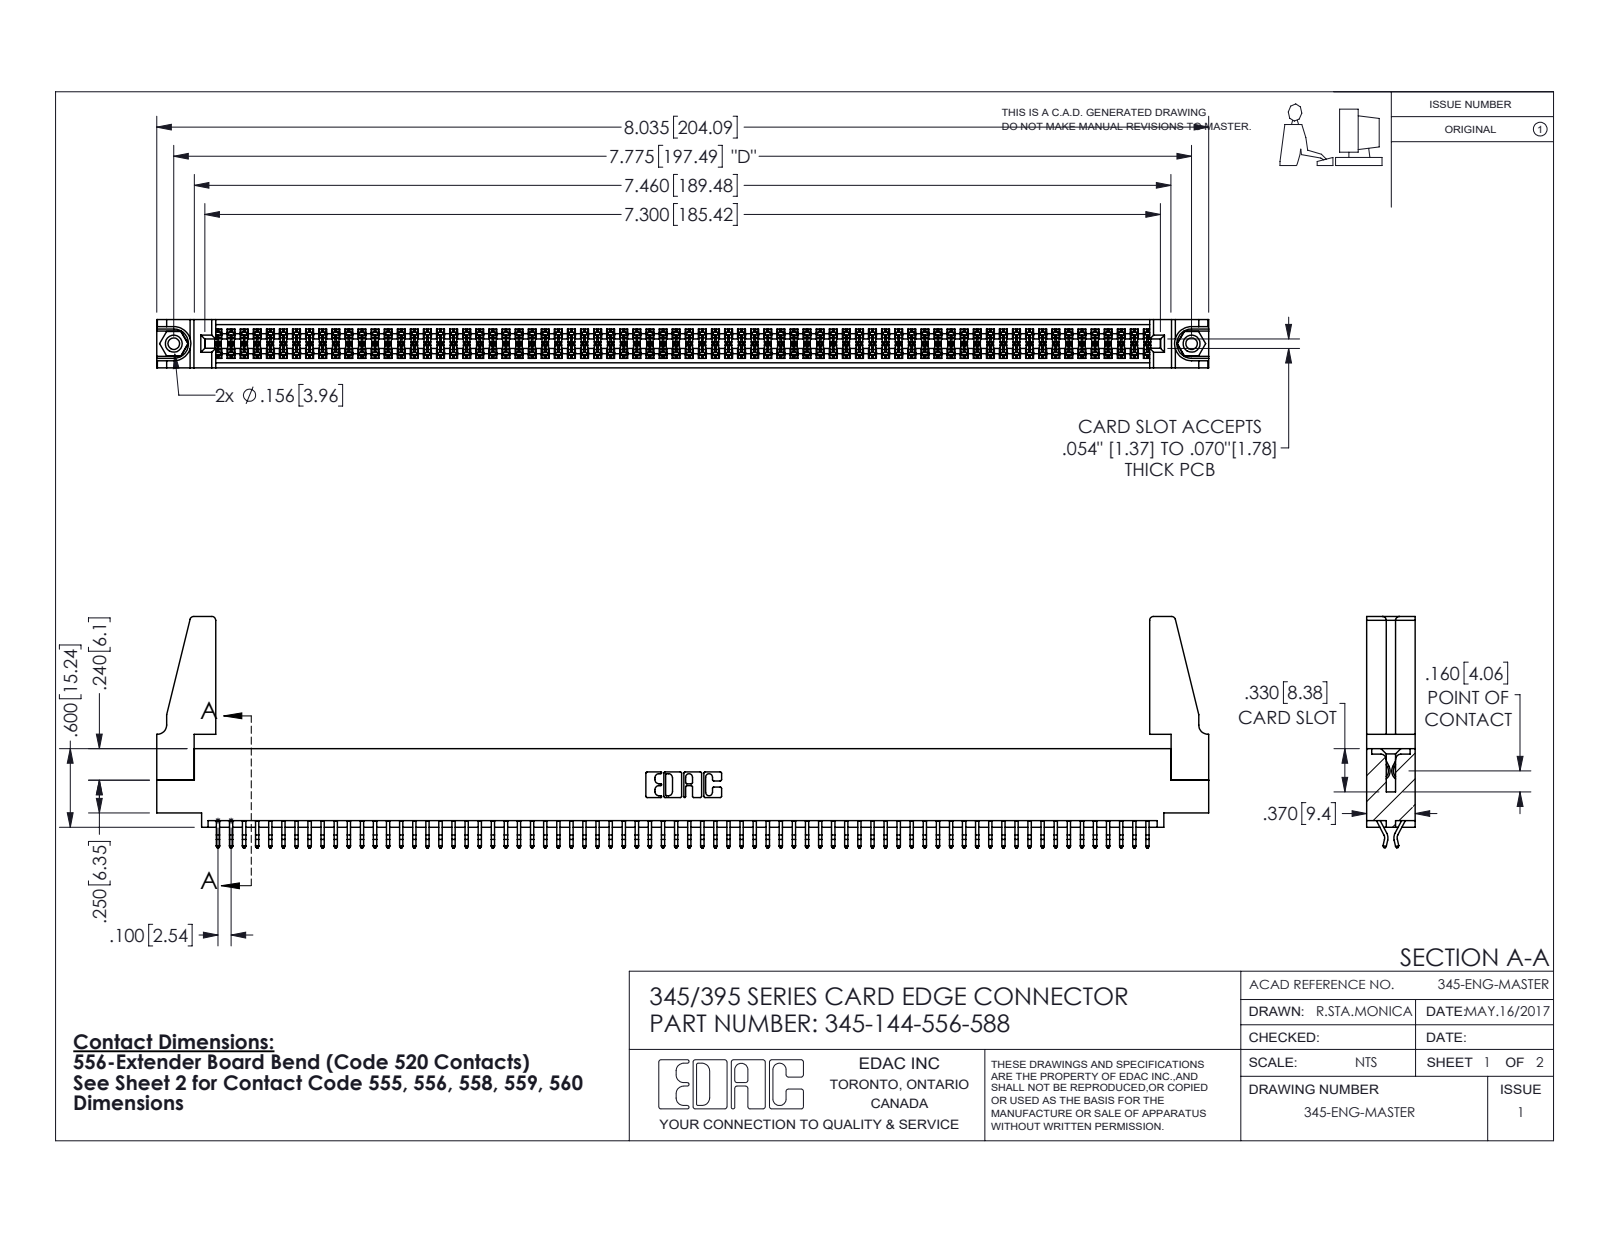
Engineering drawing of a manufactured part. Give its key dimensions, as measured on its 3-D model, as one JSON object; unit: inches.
{"part_name": "345-250-001_345-250-001-102; 345-144-556-588; 345-292-001_556 Tail; 345 Part_0.110 Offset - 0.156 Dia-TH (+1 more)", "step_written_by": "SolidWorks 2016 (CONFIG_CONTROL_DESIGN)", "units": "inches", "bodies": {"solids": 149, "faces": 8318, "planar": 5484, "cylindrical": 2818, "other": 16}, "overall_size": [8.036, 1.767, 0.37], "volume_in3": 1.421, "surface_area_in2": 51.57, "round_holes": [[0.089, 2], [0.125, 2], [0.156, 2], [0.064, 1]], "round_bosses_or_shafts": [[0.155, 2]], "partial_cylinders_radius": [[0.006, 216], [0.01, 22], [0.03, 8], [0.007, 6], [0.031, 6], [0.026, 3], [0.01, 2], [0.014, 2]], "face_to_face_distances": [0.072, 0.298, 0.37, 0.025, 0.2, 0.098, 0.272, 0.225, 0.175, 0.149], "hole_center_spacings": [0.27, 7.539, 7.775]}
